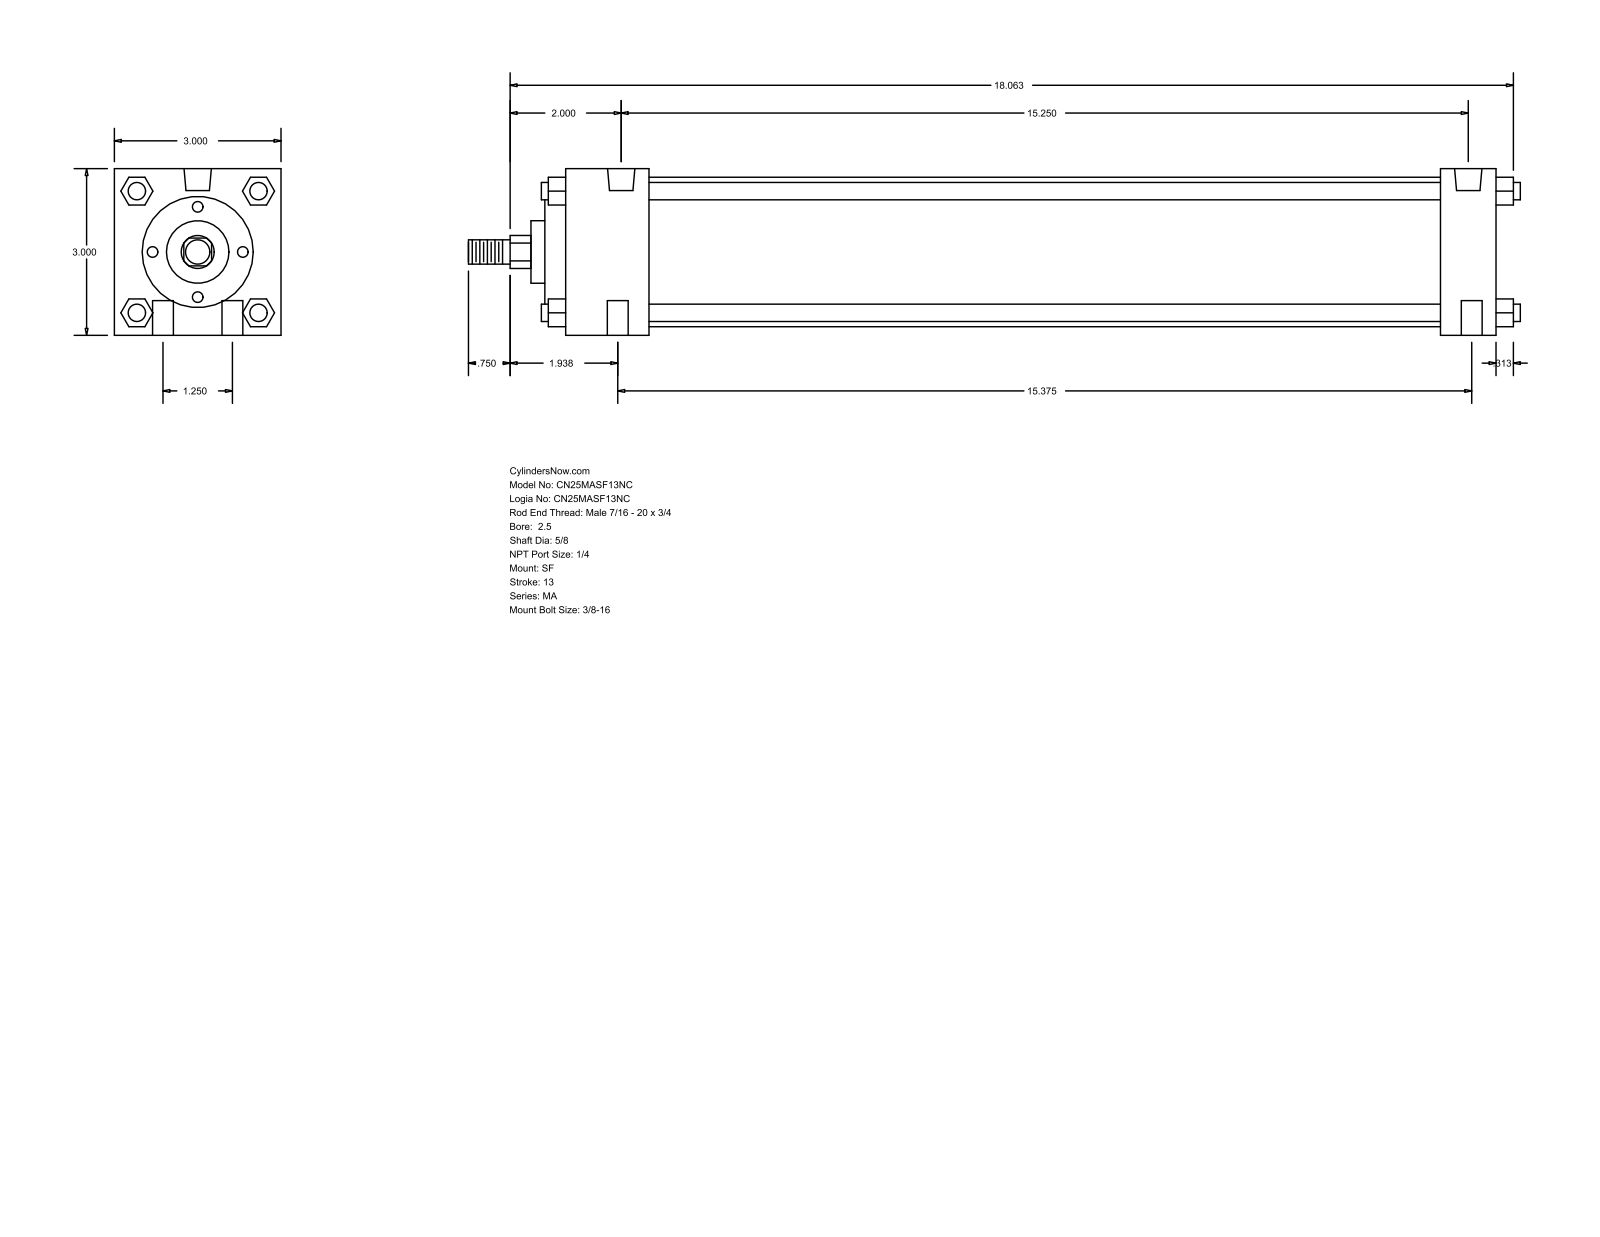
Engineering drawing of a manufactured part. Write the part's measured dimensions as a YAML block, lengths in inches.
part_name: "MA_SF__0250_0.625"
step_written_by: "GSSL Pune (CONFIG_CONTROL_DESIGN)"
units: inches
bodies: {solids: 0, faces: 126, planar: 95, cylindrical: 31, other: 0}
overall_size: [18.937, 3, 3]
round_holes:
  - {diameter: 0.375, count: 4}
  - {diameter: 0.313, count: 2}
  - {diameter: 0.492, count: 2}
round_bosses_or_shafts:
  - {diameter: 0.313, count: 4}
  - {diameter: 2.69, count: 1}
  - {diameter: 2, count: 1}
  - {diameter: 1.125, count: 1}
  - {diameter: 0.625, count: 1}
  - {diameter: 0.437, count: 1}
partial_cylinders:
  - {radius: 0.297, count: 1}
face_to_face_distances: [3, 16.75, 1, 15.75, 1.5, 14.25, 15.25, 0.5, 0.375, 1.875]
hole_center_spacings: [0.628, 15.325, 1.25, 15.25, 15.375, 15.426]
